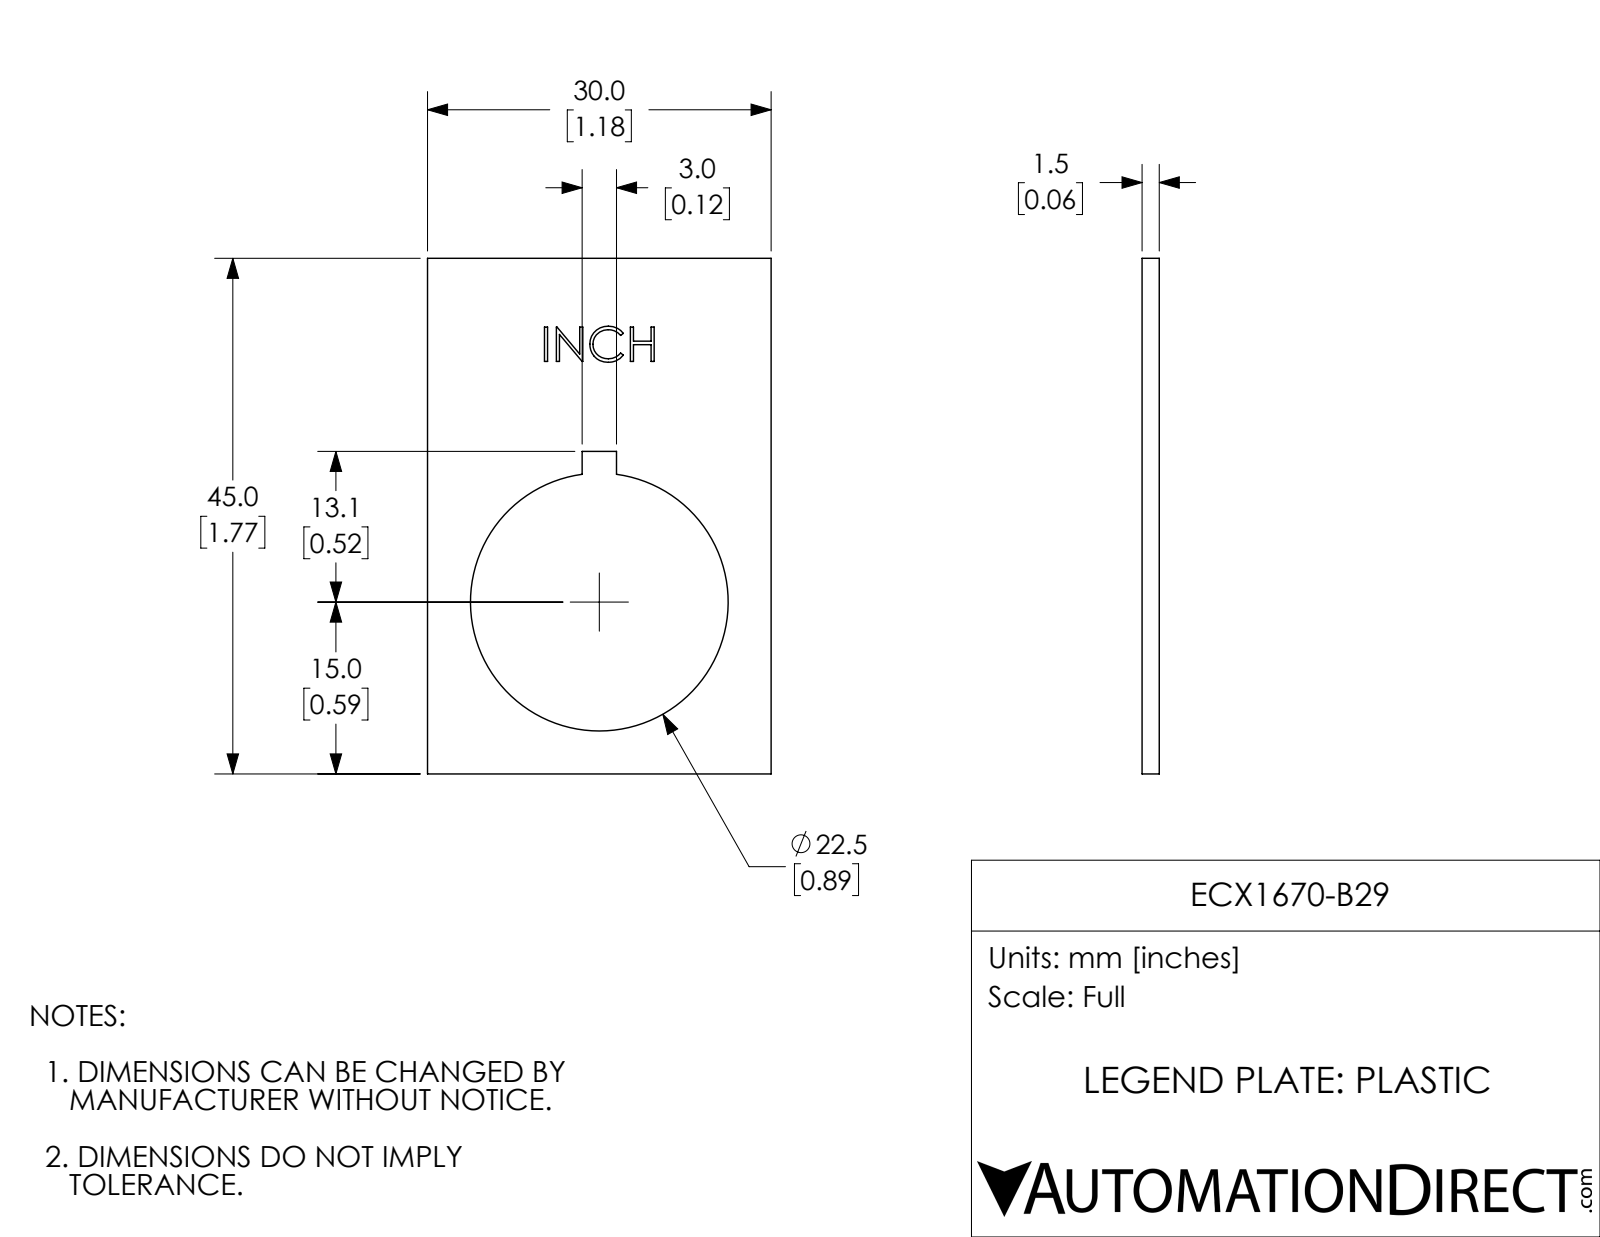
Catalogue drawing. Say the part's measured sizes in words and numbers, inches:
The part is named "ECX1670-B29". Its 3-D file was written by "SolidWorks 2017 (AUTOMOTIVE_DESIGN)". It is 1 solid with 53 faces: 41 planar, 3 cylindrical and 9 other. Overall it measures 1.772 by 1.181 by 0.059 inches. Its volume is 0.087 cubic inches and its surface area 3.459 square inches. Round holes: 1 of diameter 0.886. The main face-to-face distances are 0.059, 1.181, 1.772, 0.058, 0.531, 0.65, 1.108, 0.663, 0.118, 0.367.
